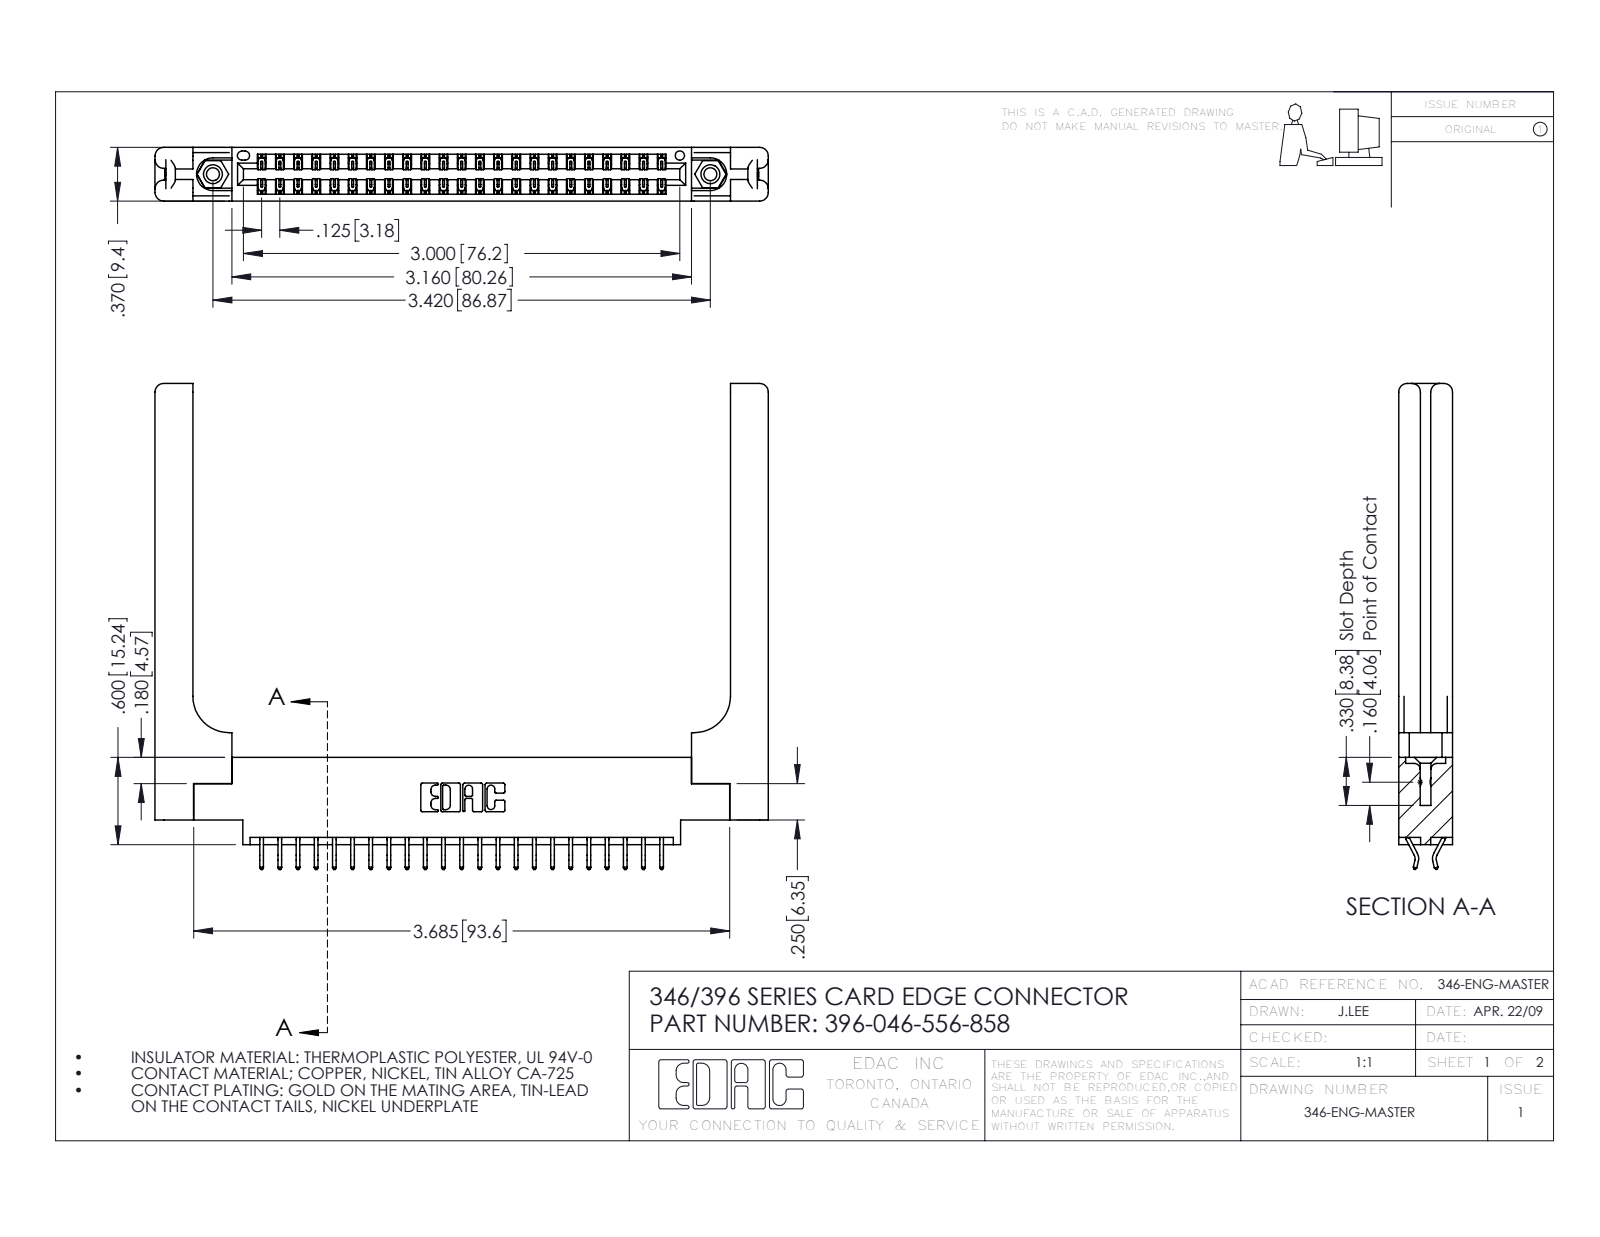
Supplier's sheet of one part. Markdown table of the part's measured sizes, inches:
| quantity | value |
| --- | --- |
| part name | 345-250-001_345-250-001-102; 396-046-556-858; 346-220-058_345-220-058; 346 Part_0.170 Offset - 0.156 Dia-TH (+1 more) |
| STEP written by | SolidWorks 2016 (CONFIG_CONTROL_DESIGN) |
| units | inches |
| bodies | 51 solids, 3050 faces (2022 planar, 968 cylindrical, 60 other) |
| overall size | 4.216 × 3.34 × 0.37 |
| volume | 1.076 in³ |
| surface area | 29.06 in² |
| round holes (diameter × count) | 0.089 × 2, 0.125 × 2, 0.156 × 2, 0.064 × 1 |
| round bosses / shafts (diameter × count) | 0.155 × 2 |
| partial cylindrical surfaces (radius × count) | 0.006 × 69, 0.01 × 22, 0.06 × 16, 0.007 × 6, 0.031 × 6, 0.026 × 3, 0.01 × 2, 0.014 × 2 |
| main face-to-face distances | 0.37, 0.072, 0.048, 0.322, 0.148, 0.15, 0.25, 0.025, 0.298, 0.077 |
| hole center spacings | 0.246, 3.212, 3.42 |
